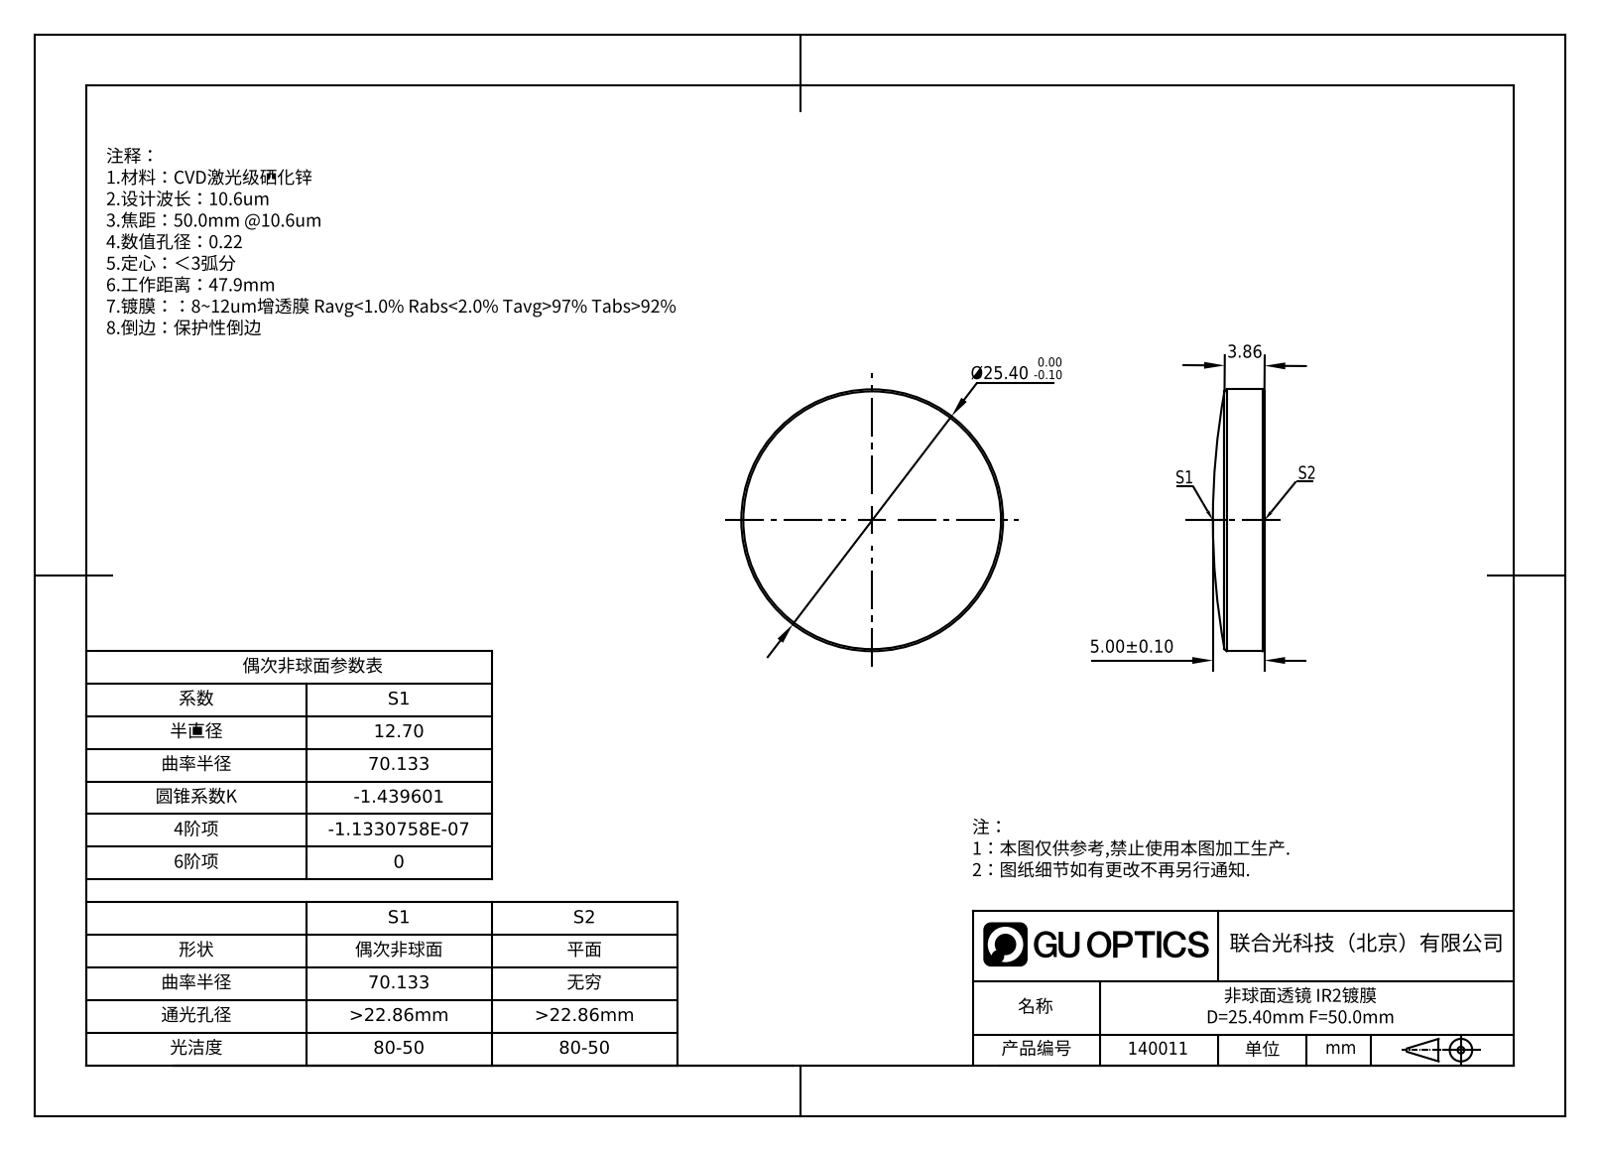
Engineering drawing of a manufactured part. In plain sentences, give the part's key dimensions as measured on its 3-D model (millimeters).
The part is named "140011". Its 3-D file was written by "SolidWorks 2020 (CONFIG_CONTROL_DESIGN)". It is 1 solid with 5 faces: 1 planar, 2 cylindrical and 2 other. Overall it measures 25.4 by 25.4 by 5 millimeters. Its volume is 2 244 cubic millimeters and its surface area 1 325 square millimeters. Round bosses or shafts: 1 of diameter 25.4.
